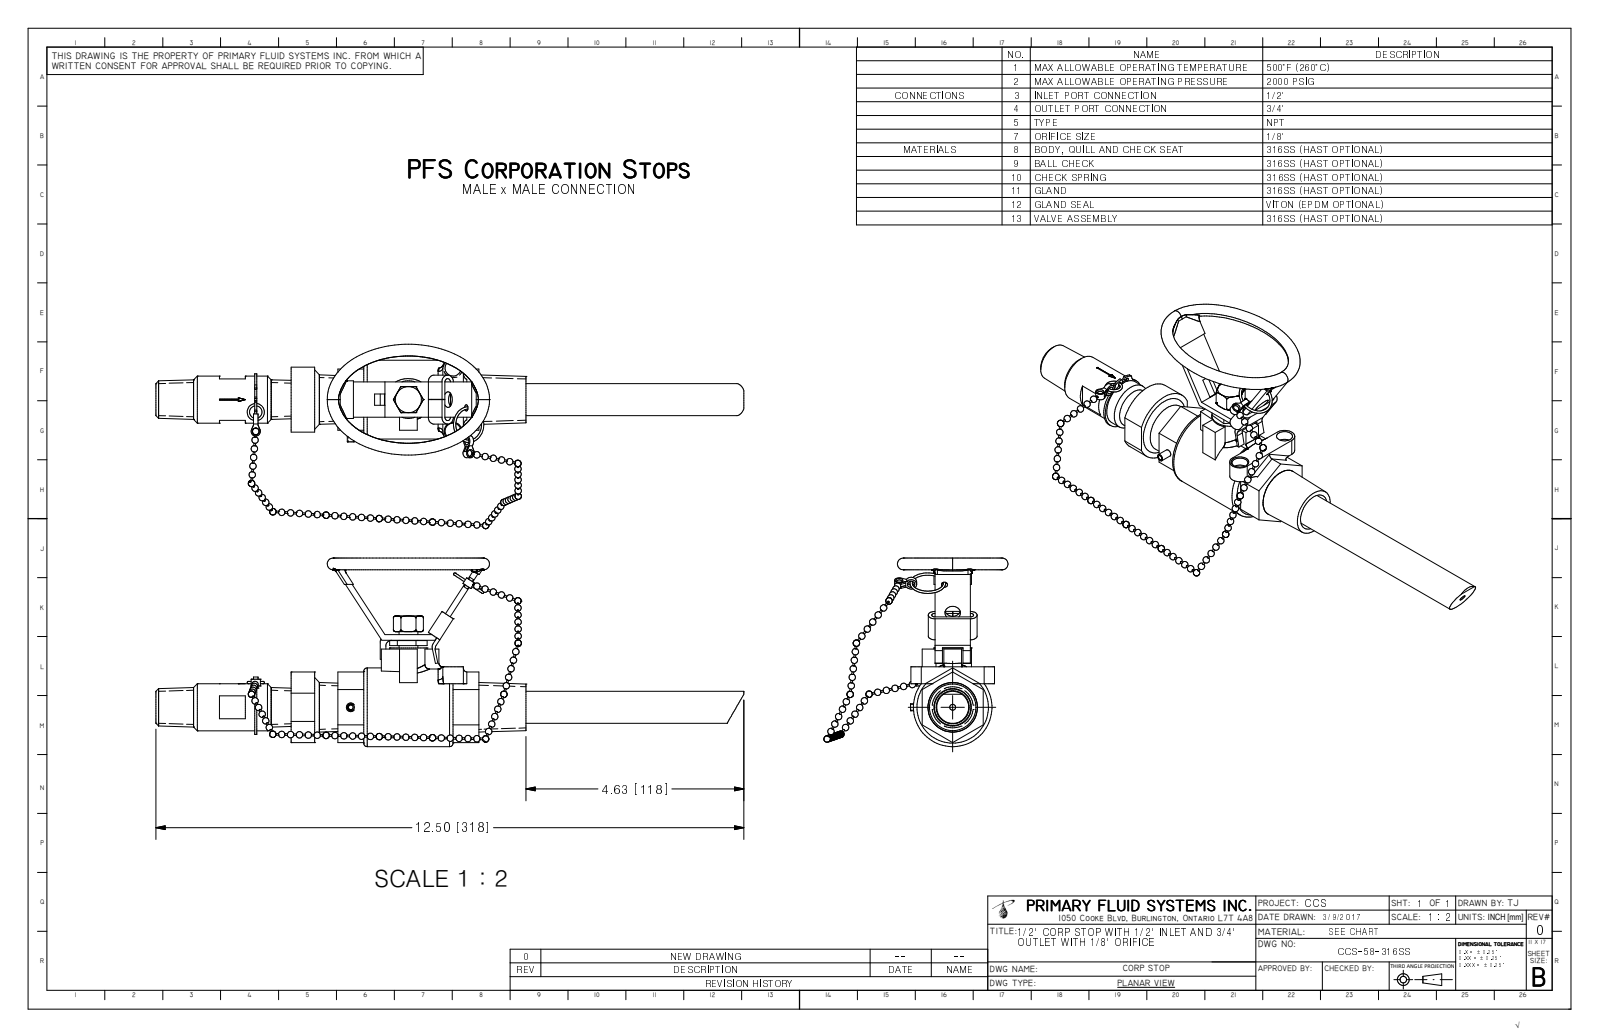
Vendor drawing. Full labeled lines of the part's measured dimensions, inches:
Part name (STEP PRODUCT): CCS-58-316SS_R0
STEP written by: Autodesk Inventor 2009 (AUTOMOTIVE_DESIGN)
Units: inches
Bodies: 0 solids, 417 faces (178 planar, 42 cylindrical, 197 other)
Overall size (bounding box): 12.5 × 4 × 3.913
Round holes (diameter × count): ⌀0.079 ×1, ⌀0.125 ×1, ⌀0.25 ×1, ⌀0.469 ×1
Round bosses / shafts (diameter × count): ⌀1.67 ×1, ⌀1.094 ×1, ⌀1 ×1, ⌀0.8 ×1, ⌀0.679 ×1, ⌀0.4 ×1, ⌀0.15 ×1
Partial cylindrical surfaces — rounded edges, fillets, slot ends (radius × count): R0.075 ×4, R0.043 ×2, R0.05 ×2, R0.145 ×2, R0.15 ×2, R0.157 ×2, R0.125 ×1, R0.165 ×1
Main face-to-face distances: 1.299, 0.12, 0.55, 0.275, 1.025, 0.12, 0.993, 0.16, 2.45, 0.038
Hole centre spacings: 0.535
